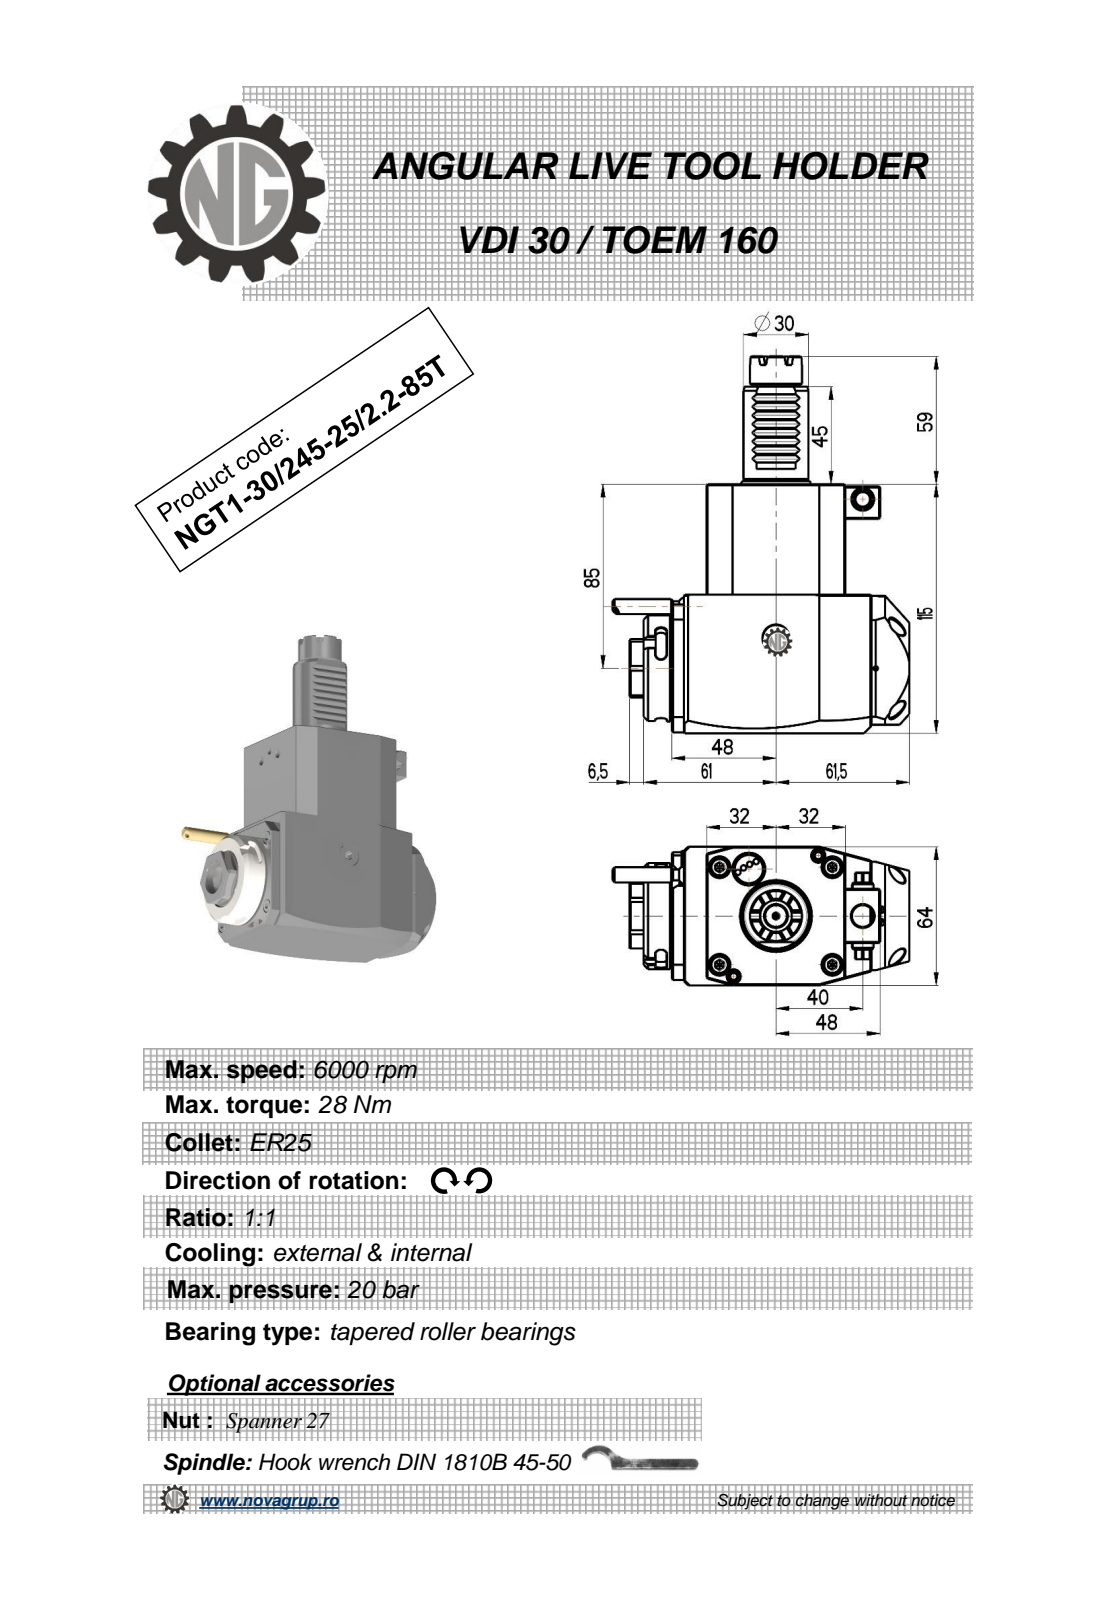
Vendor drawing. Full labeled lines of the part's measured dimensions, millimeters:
Part name (STEP PRODUCT): NGT1_30_245_25_1_2_85T
STEP written by: PRO/ENGINEER BY PARAMETRIC TECHNOLOGY CORPORATION, 2010280 (CONFIG_CONTROL_DESIGN)
Units: millimetres
Bodies: 1 solid, 374 faces (210 planar, 82 cylindrical, 82 other)
Overall size (bounding box): 174 × 136.88 × 64
Volume: 673 046 mm³ · Surface area: 57 601 mm²
Round holes (diameter × count): ⌀2.5 ×1, ⌀3 ×1, ⌀8.5 ×1, ⌀9.5 ×1, ⌀10 ×1, ⌀18 ×1
Round bosses / shafts (diameter × count): ⌀8 ×2, ⌀49 ×1, ⌀42 ×1, ⌀30 ×1, ⌀24 ×1, ⌀17.7 ×1, ⌀15.2 ×1, ⌀10 ×1
Partial cylindrical surfaces — rounded edges, fillets, slot ends (radius × count): R0.3 ×8, R2.5 ×6, R180 ×2, R3.85 ×1, R4.5 ×1, R15 ×1, R21.5 ×1, R33.5 ×1
Main face-to-face distances: 64, 115, 16, 80, 13, 51, 109.5, 93.5, 29.5, 72.18
Hole centre spacings: 34.25, 51.62, 76.5
